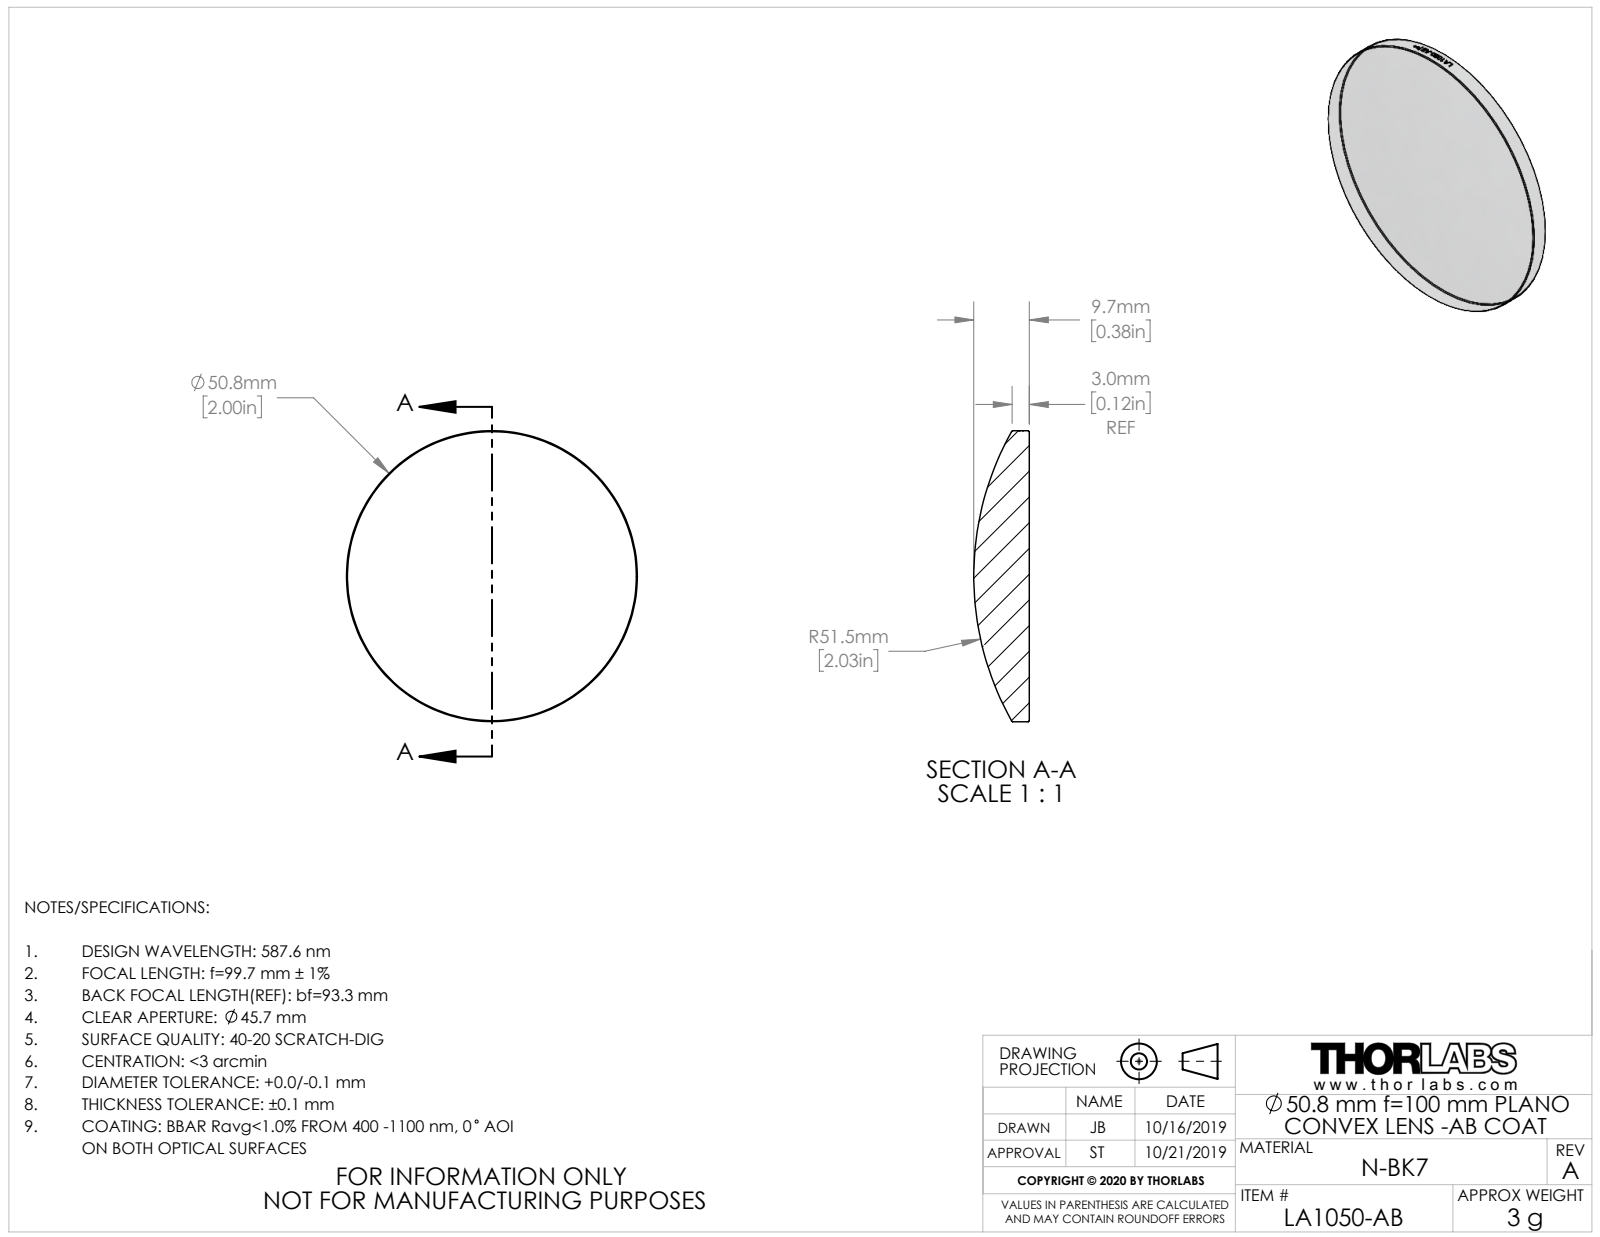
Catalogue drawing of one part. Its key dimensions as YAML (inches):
part_name: "TTN195797-E0W"
step_written_by: "SolidWorks 2018 (CONFIG_CONTROL_DESIGN)"
units: inches
bodies: {solids: 1, faces: 28, planar: 1, cylindrical: 21, other: 6}
overall_size: [2, 2, 0.381]
volume: 0.794
surface_area: 7.208
round_bosses_or_shafts:
  - {diameter: 2, count: 1}
